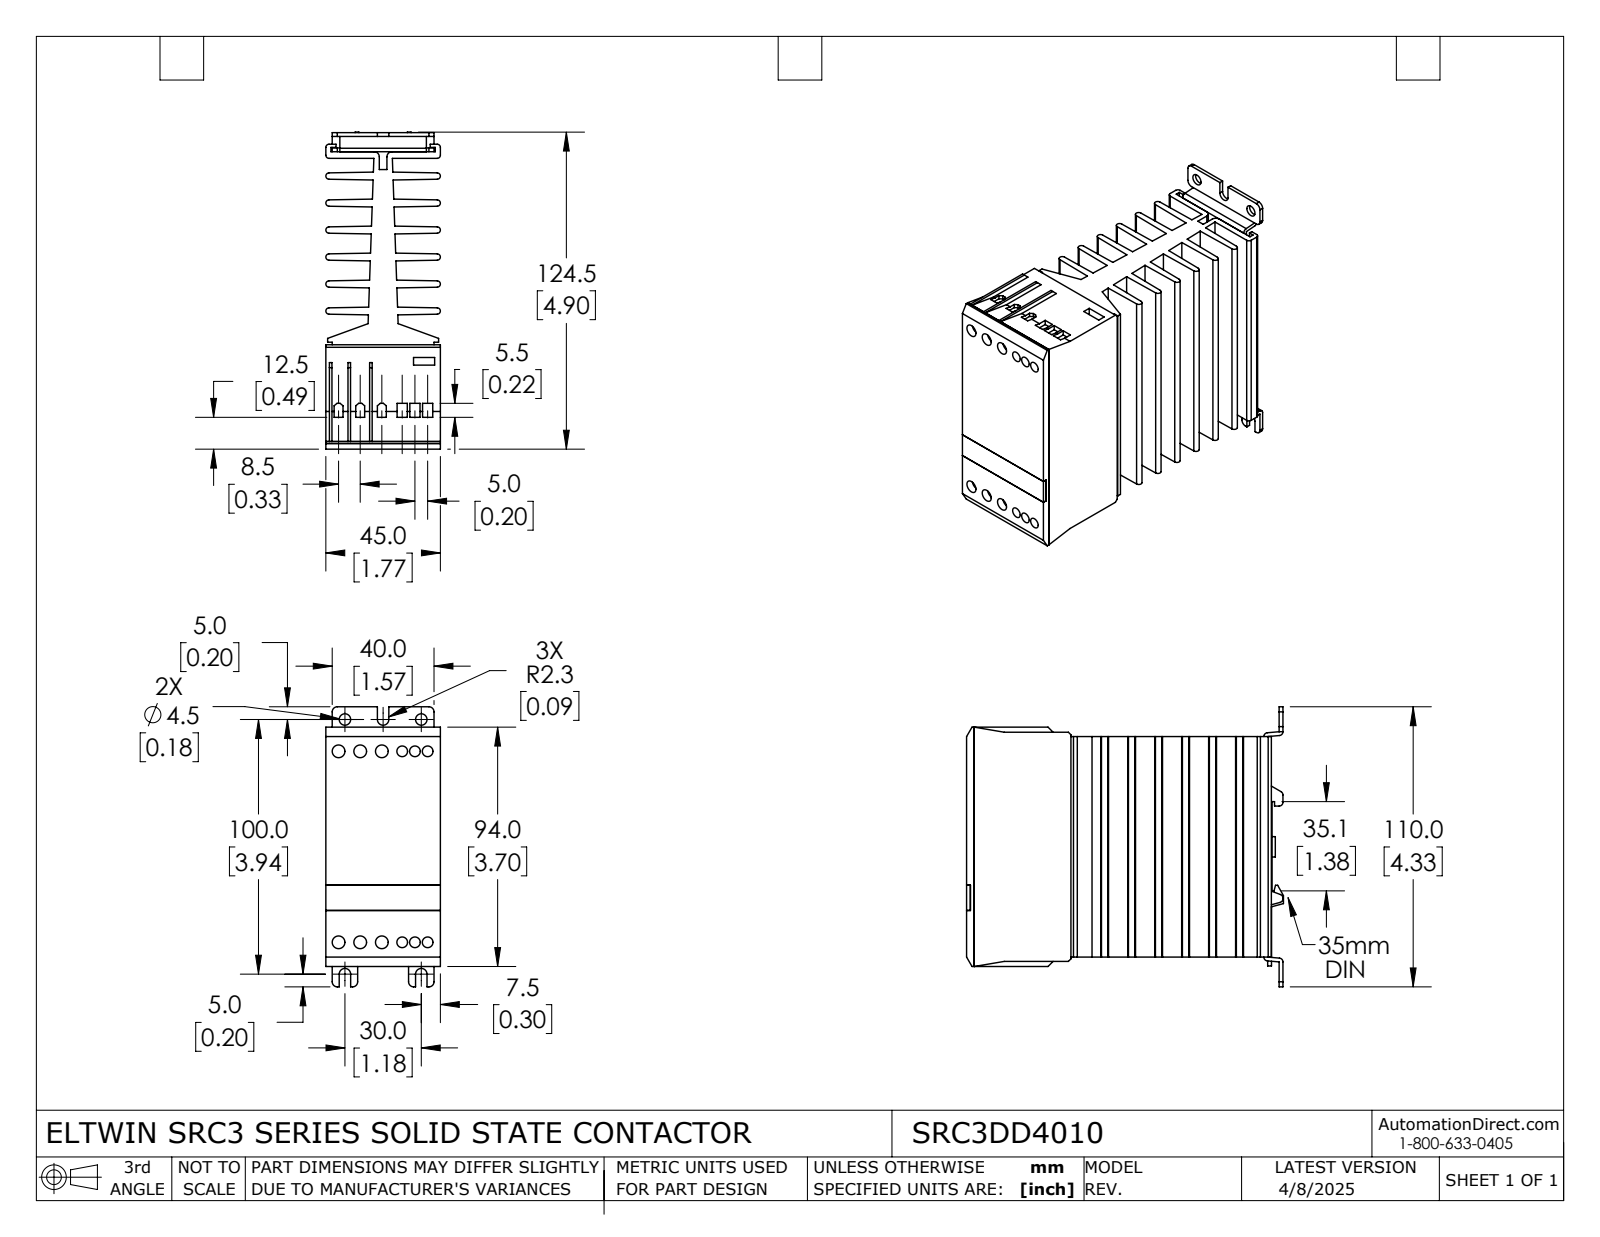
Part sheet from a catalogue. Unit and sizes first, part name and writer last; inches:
Units: inches
Overall size (bounding box): 4.902 × 4.331 × 1.772
Round holes (diameter × count): ⌀0.165 ×6, ⌀0.173 ×6, ⌀0.197 ×6, ⌀0.236 ×6, ⌀0.177 ×2
Round bosses / shafts (diameter × count): ⌀0.315 ×1
Partial cylindrical surfaces — rounded edges, fillets, slot ends (radius × count): R0.079 ×18, R0.049 ×16, R0.059 ×10, R0.051 ×4, R0.089 ×3
Main face-to-face distances: 0.417, 0.835, 0.127, 1.252, 0.29, 0.544, 0.707, 0.962, 1.669, 1.125
Hole centre spacings: 2.953, 0.197, 0.335, 2.959, 2.972, 0.502, 1.181, 3.446
Volume: 18.87 in³ · Surface area: 165.9 in²
Bodies: 5 solids, 427 faces (316 planar, 111 cylindrical, 0 other)
Part name (STEP PRODUCT): SRC3DD4010
STEP written by: SolidWorks 2021 (AUTOMOTIVE_DESIGN)
